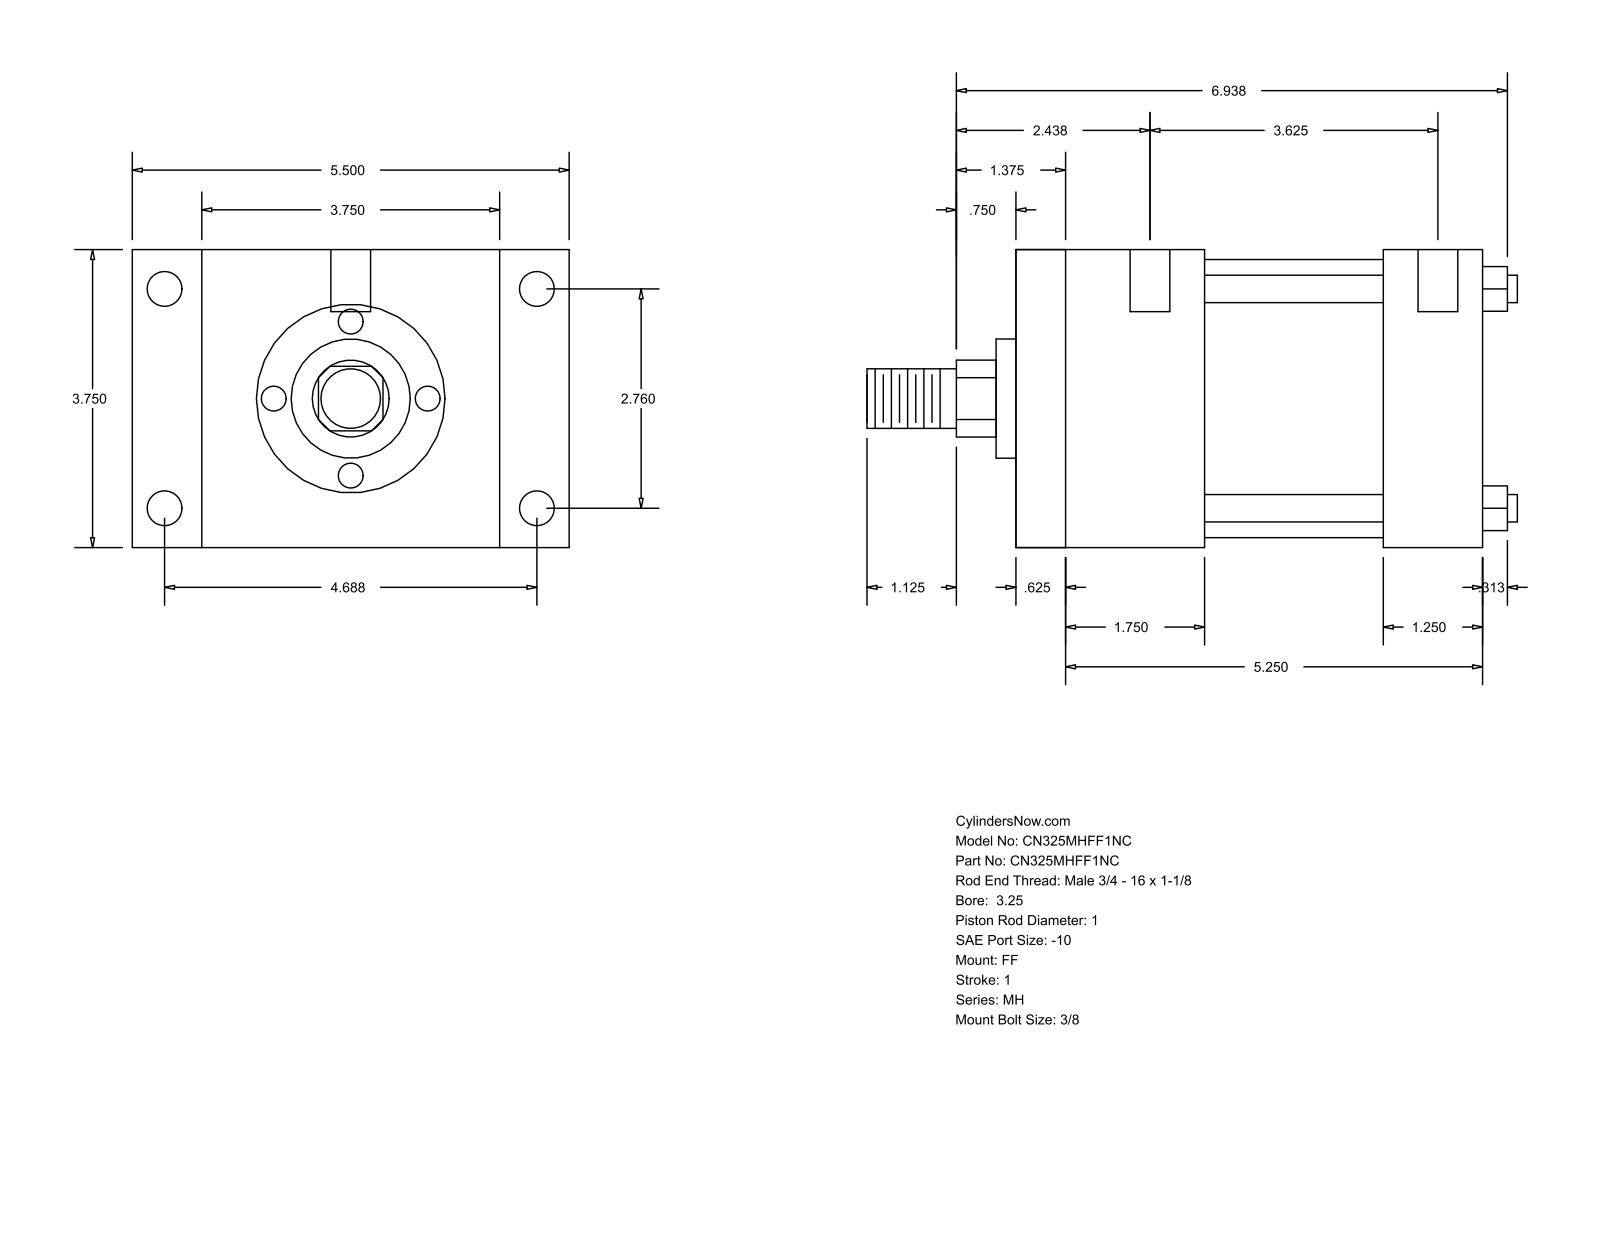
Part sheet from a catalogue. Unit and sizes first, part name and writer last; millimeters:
Units: millimetres
Overall size (bounding box): 207.96 × 139.7 × 95.25
Round holes (diameter × count): ⌀5.56 ×4, ⌀11.13 ×4, ⌀12.7 ×2
Round bosses / shafts (diameter × count): ⌀8.76 ×4, ⌀88.9 ×1, ⌀38.1 ×1, ⌀25.4 ×1, ⌀19.05 ×1
Partial cylindrical surfaces — rounded edges, fillets, slot ends (radius × count): R12.29 ×1
Main face-to-face distances: 95.24, 149.23, 15.87, 133.36, 22.23, 117.47, 117.48, 101.61, 31.75, 60.33
Hole centre spacings: 70.1, 98.42, 119.06, 138.16, 1.58, 4.76, 92.08, 93.66
Bodies: 0 solids, 92 faces (64 planar, 28 cylindrical, 0 other)
Part name (STEP PRODUCT): MH_FF__0325_1
STEP written by: GSSL Pune (CONFIG_CONTROL_DESIGN)
